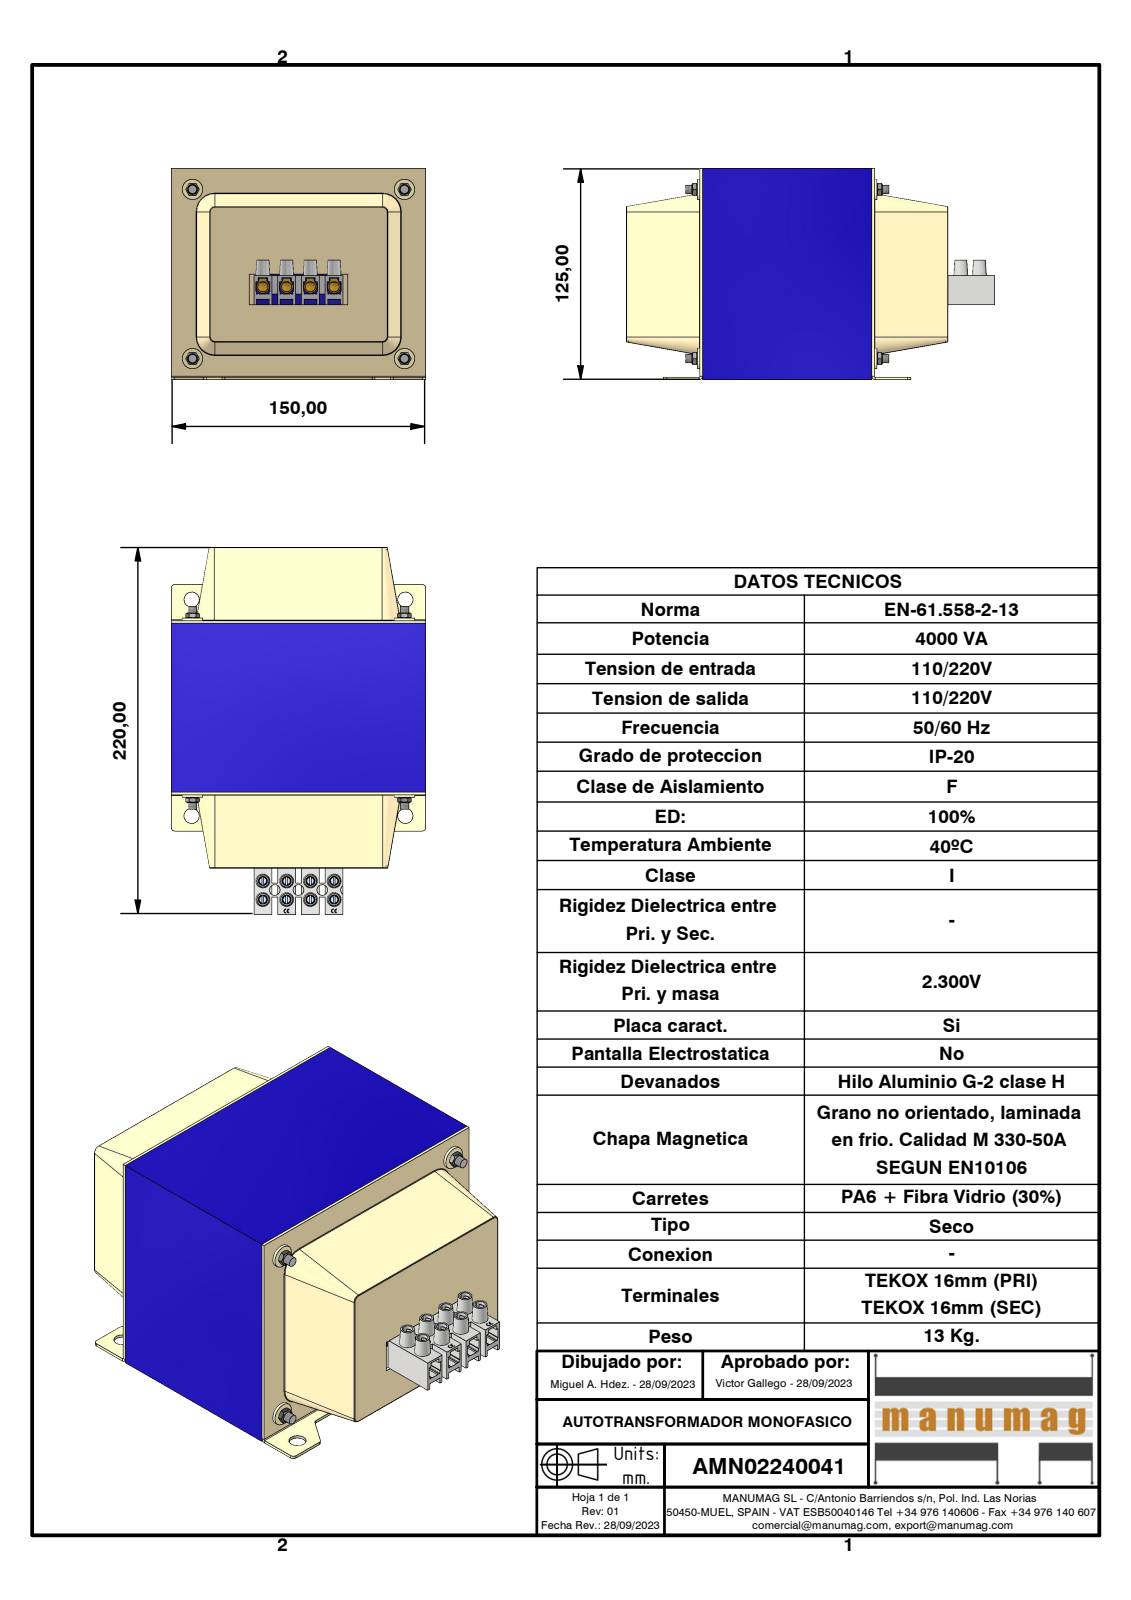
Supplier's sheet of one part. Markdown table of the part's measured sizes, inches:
| quantity | value |
| --- | --- |
| part name | AMN02240041; EI150 x 125 - 100 (RC50) Azul; TAPA RC50 CIEGA; TAPA RC50 VENTANA 4 ELEMENTOS 16 (+8 more) |
| STEP written by | Autodesk Inventor 2023 (AUTOMOTIVE_DESIGN) |
| units | inches |
| bodies | 44 solids, 1637 faces (1104 planar, 222 cylindrical, 311 other) |
| overall size | 8.563 × 5.906 × 4.921 |
| volume | 95.38 in³ |
| surface area | 473.8 in² |
| round holes (diameter × count) | 0.128 × 12, 0.217 × 8, 0.236 × 8, 0.197 × 4, 0.315 × 4, 0.354 × 4, 0.248 × 3 |
| round bosses / shafts (diameter × count) | 0.157 × 8, 0.472 × 4, 0.232 × 4 |
| partial cylindrical surfaces (radius × count) | 0.015 × 16, 0.108 × 16, 0.079 × 14, 0.032 × 8, 0.118 × 8, 0.009 × 6, 0.004 × 4, 0.032 × 4 |
| main face-to-face distances | 3.937, 0.984, 0.059, 1.713, 4.921, 5.709, 1.969, 2.953, 4.394, 1.654 |
| hole center spacings | 0.551, 1.102, 0.347, 0.354, 0.701, 0.433, 0.853, 0.856 |
